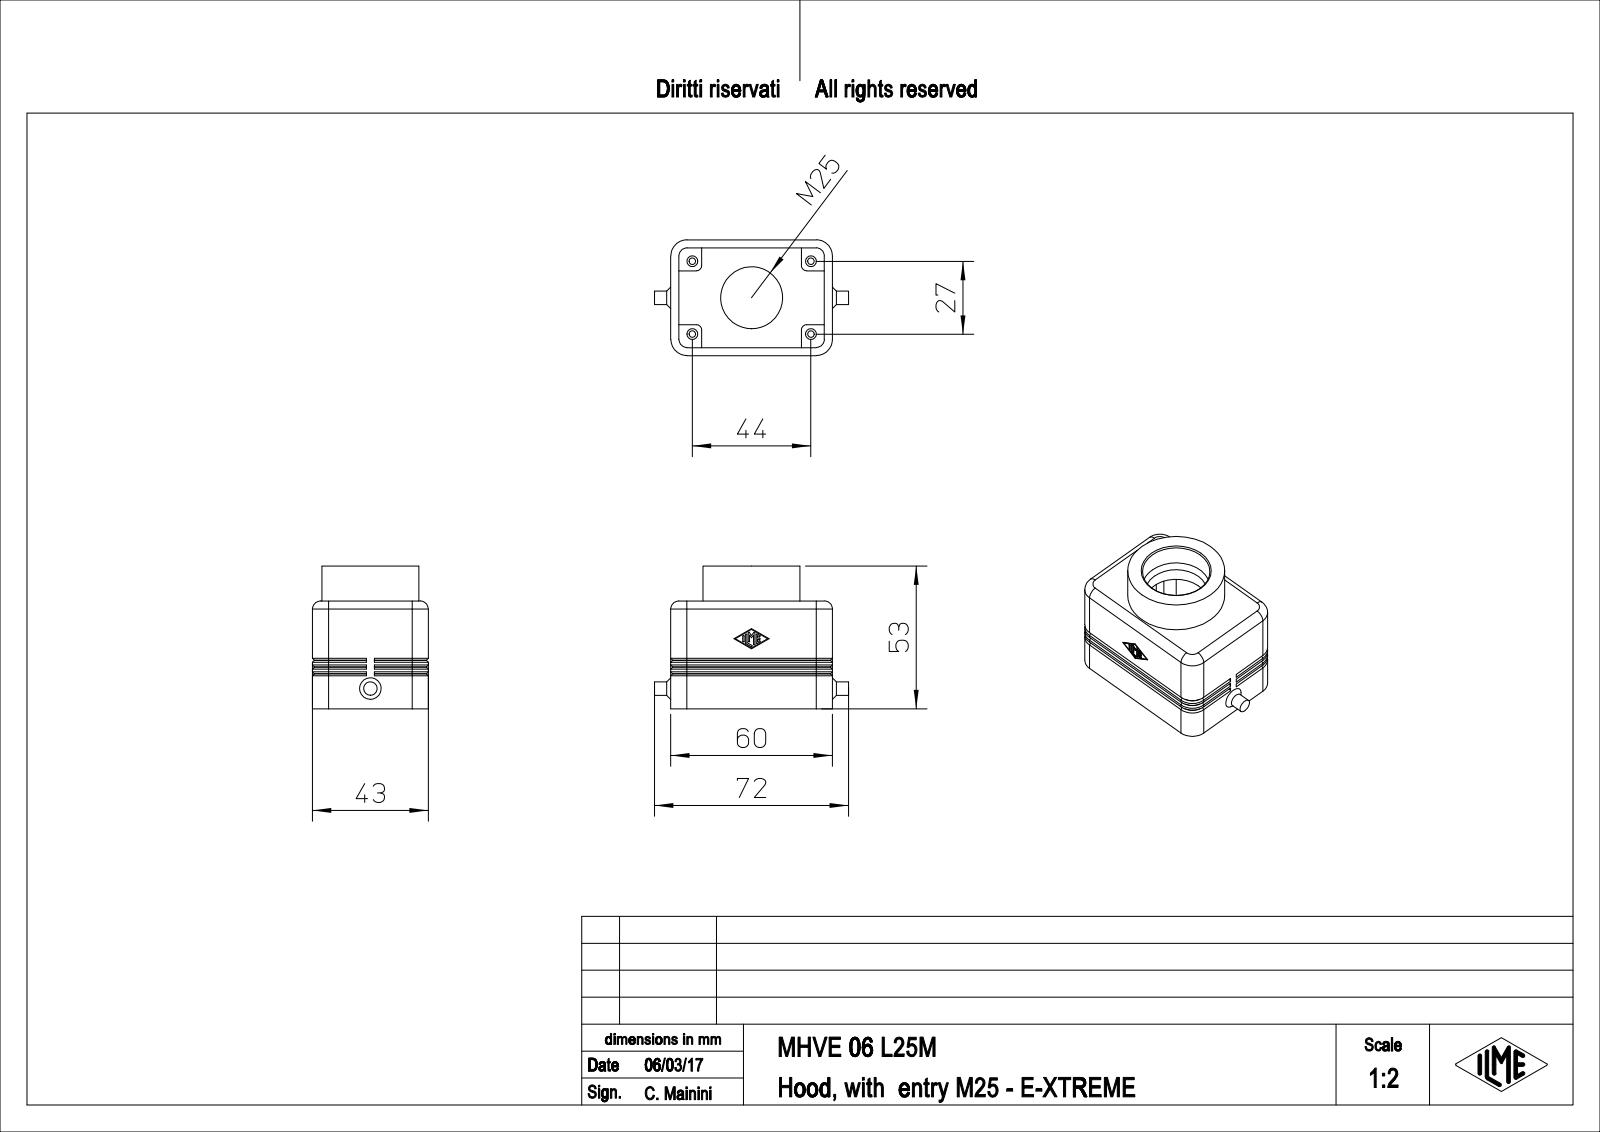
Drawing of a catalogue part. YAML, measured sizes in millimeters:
part_name: "MHVE_06_L25M"
step_written_by: "PTC Creo Elements/Direct Modeling 19.0E 27-Jun-2016 (C) Parametric Technology GmbH (AUTOMOTIVE_DESIGN)"
units: millimeters
bodies: {solids: 1, faces: 263, planar: 139, cylindrical: 80, other: 44}
overall_size: [72, 53, 43]
volume: 41165
surface_area: 21909
round_holes:
  - {diameter: 2.46, count: 4}
  - {diameter: 4, count: 4}
  - {diameter: 23, count: 1}
  - {diameter: 25, count: 1}
round_bosses_or_shafts:
  - {diameter: 36, count: 1}
  - {diameter: 5, count: 1}
partial_cylinders:
  - {radius: 0.25, count: 14}
  - {radius: 3, count: 8}
  - {radius: 2, count: 4}
  - {radius: 5.3, count: 4}
  - {radius: 6, count: 4}
face_to_face_distances: [3, 40, 37, 57, 43, 11.5, 8.5, 60, 54, 48.5]
hole_center_spacings: [25.81, 27, 44, 51.62]
